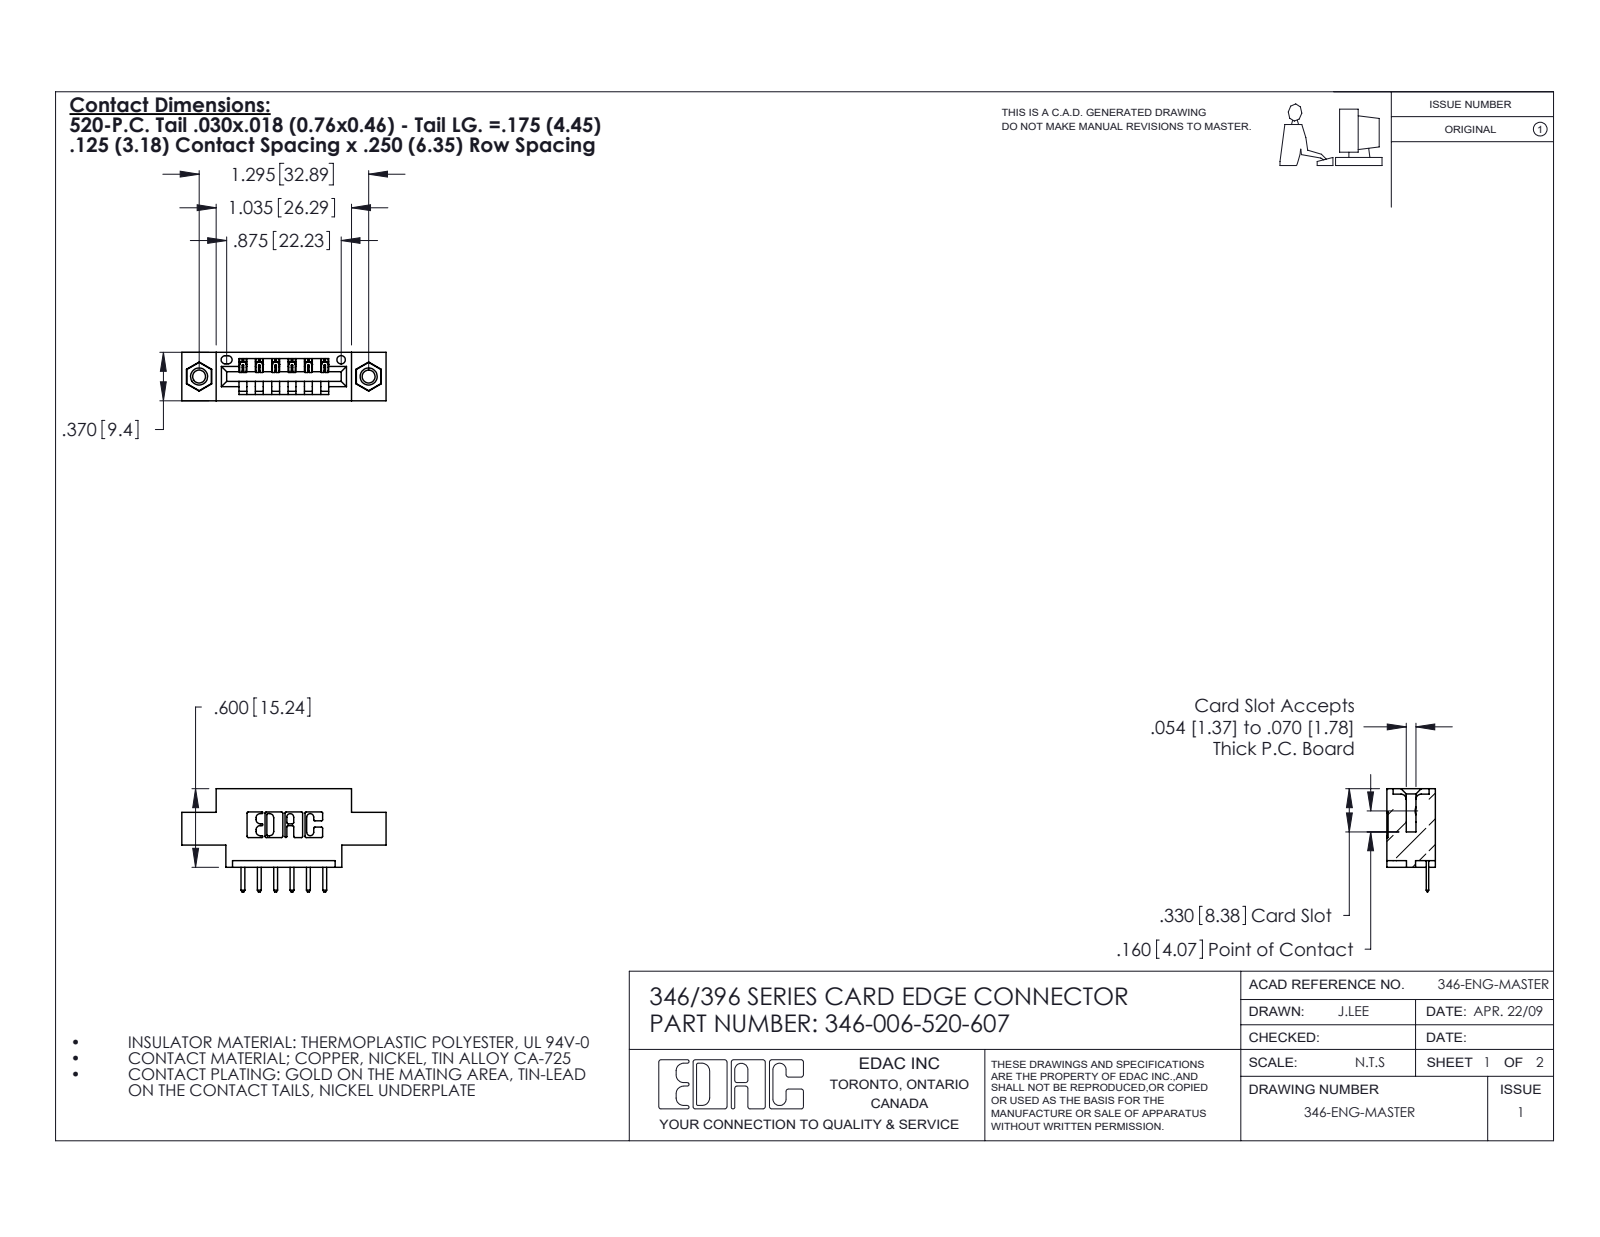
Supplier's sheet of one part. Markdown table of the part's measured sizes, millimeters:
| quantity | value |
| --- | --- |
| part name | 345-292-001_345-293-120; 346 Part_0.170 Offset - 0.156 Dia-TI; 346-006-520-607; 345-250-001_345-250-005-103 |
| STEP written by | SolidWorks 2020 (CONFIG_CONTROL_DESIGN) |
| units | millimeters |
| bodies | 9 solids, 558 faces (364 planar, 178 cylindrical, 16 other) |
| overall size | 39.6 × 20 × 9.4 |
| volume | 3 360 mm³ |
| surface area | 3 948 mm² |
| round holes (diameter × count) | 2.5 × 2, 3.2 × 2, 4 × 2, 1.6 × 1 |
| round bosses / shafts (diameter × count) | 3.9 × 2 |
| partial cylindrical surfaces (radius × count) | 0.3 × 22, 0.3 × 14, 0.2 × 12, 0.2 × 6, 0.8 × 6, 0.7 × 3, 0.8 × 2, 1 × 2 |
| main face-to-face distances | 6.4, 9.4, 1.2, 8.2, 5.6, 3.8, 2.5, 4.4, 3.2, 4.7 |
| hole center spacings | 6.2, 27.7, 32.9 |
